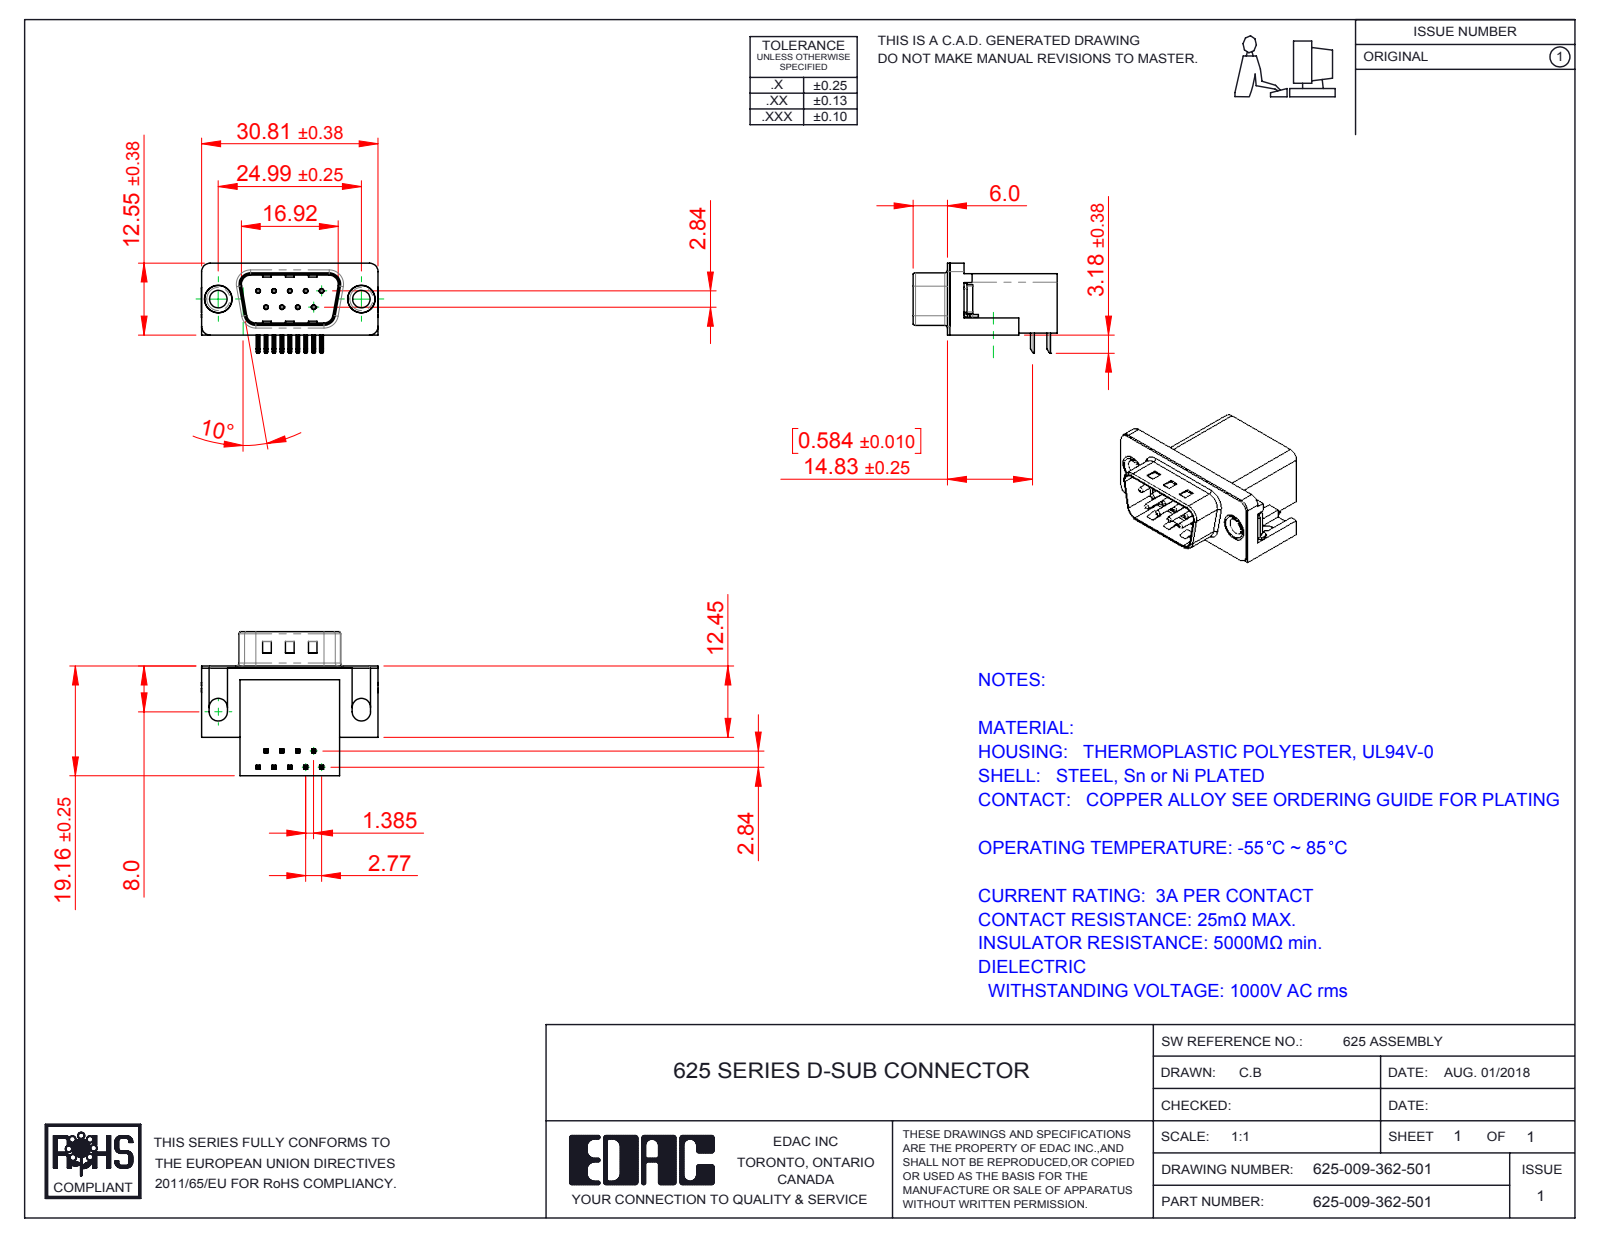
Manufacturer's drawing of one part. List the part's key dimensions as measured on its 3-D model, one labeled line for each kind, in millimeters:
Part name (STEP PRODUCT): 625 Contact Bottom; 625 Housing_9 Socket; 625-009-362-501; 625 Non Board Mount (+3 more)
STEP written by: SolidWorks 2016 (CONFIG_CONTROL_DESIGN)
Units: millimetres
Bodies: 15 solids, 951 faces (575 planar, 295 cylindrical, 81 other)
Overall size (bounding box): 30.89 × 25.16 × 15.73
Volume: 4 436 mm³ · Surface area: 4 794 mm²
Round holes (diameter × count): ⌀0.35 ×9, ⌀0.8 ×9, ⌀3.05 ×2, ⌀4 ×2, ⌀4.8 ×2, ⌀5 ×2
Round bosses / shafts (diameter × count): ⌀0.75 ×9, ⌀4.9 ×2, ⌀4.75 ×2, ⌀3.85 ×2
Partial cylindrical surfaces — rounded edges, fillets, slot ends (radius × count): R0.25 ×44, R0.12 ×18, R1 ×16, R0.5 ×9, R1.5 ×8, R1.6 ×8, R0.9 ×4, R2 ×4
Main face-to-face distances: 0.4, 10.34, 18.76, 19.16, 2.9, 16.26, 2.5, 0.35, 10.69, 6.7
Hole centre spacings: 3.16, 2.77, 5.54, 5.03, 5.04, 8.31, 7.48, 7.49
